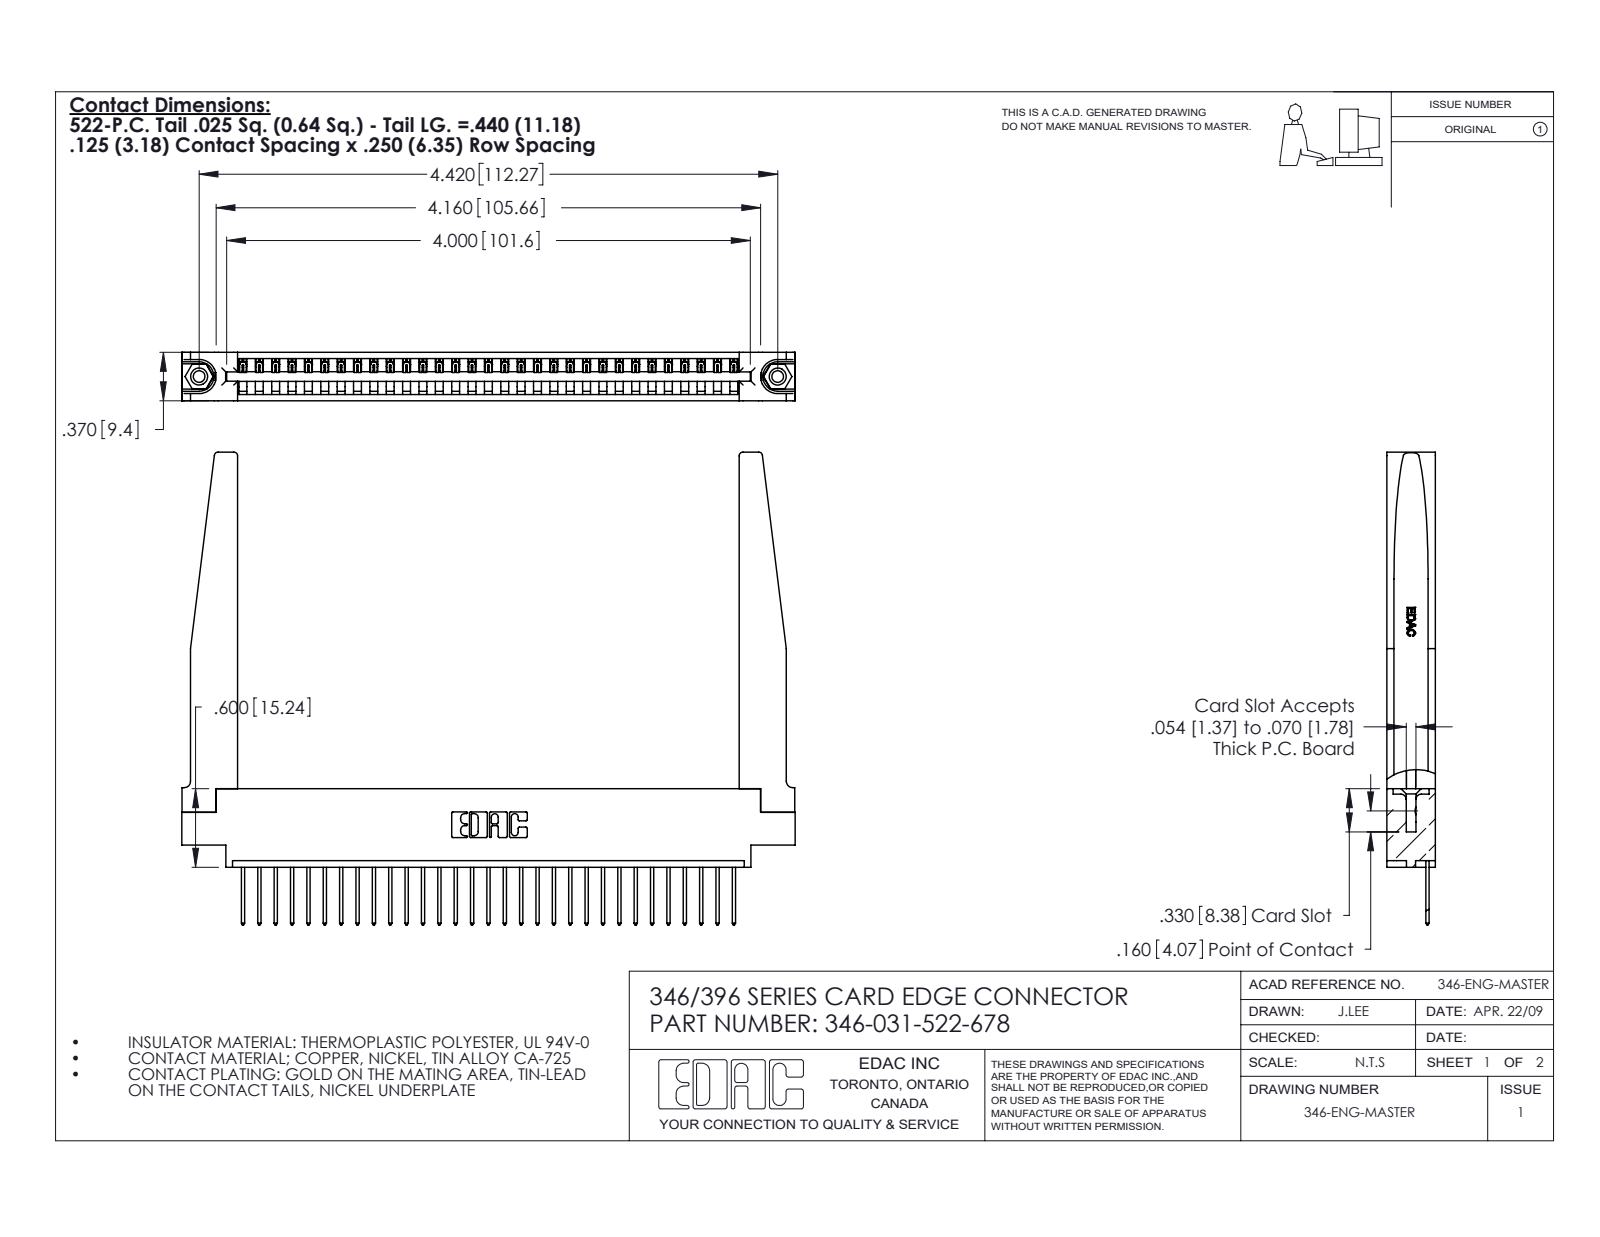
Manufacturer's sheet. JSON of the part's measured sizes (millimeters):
{"part_name": "346 Part_0.170 Offset - 0.156 Dia-TH; 346-031-522-678; 345-250-001_345-250-001-102; 345-292-001_345-293-122 (+1 more)", "step_written_by": "SolidWorks 2020 (CONFIG_CONTROL_DESIGN)", "units": "millimeters", "bodies": {"solids": 36, "faces": 2172, "planar": 1476, "cylindrical": 644, "other": 52}, "overall_size": [119, 91.7, 9.4], "volume_mm3": 18060, "surface_area_mm2": 20660, "round_holes": [[2.3, 2], [3.2, 2], [4, 2], [1.6, 1]], "round_bosses_or_shafts": [[3.9, 2]], "partial_cylinders_radius": [[0.2, 62], [0.3, 62], [0.3, 22], [0.8, 8], [0.2, 6], [0.8, 6], [0.7, 3], [0.8, 2]], "face_to_face_distances": [9.4, 1.2, 8.2, 1.8, 3.8, 3.8, 6.4, 7.6, 0.6, 5.6], "hole_center_spacings": [6.2, 107, 112.3]}
